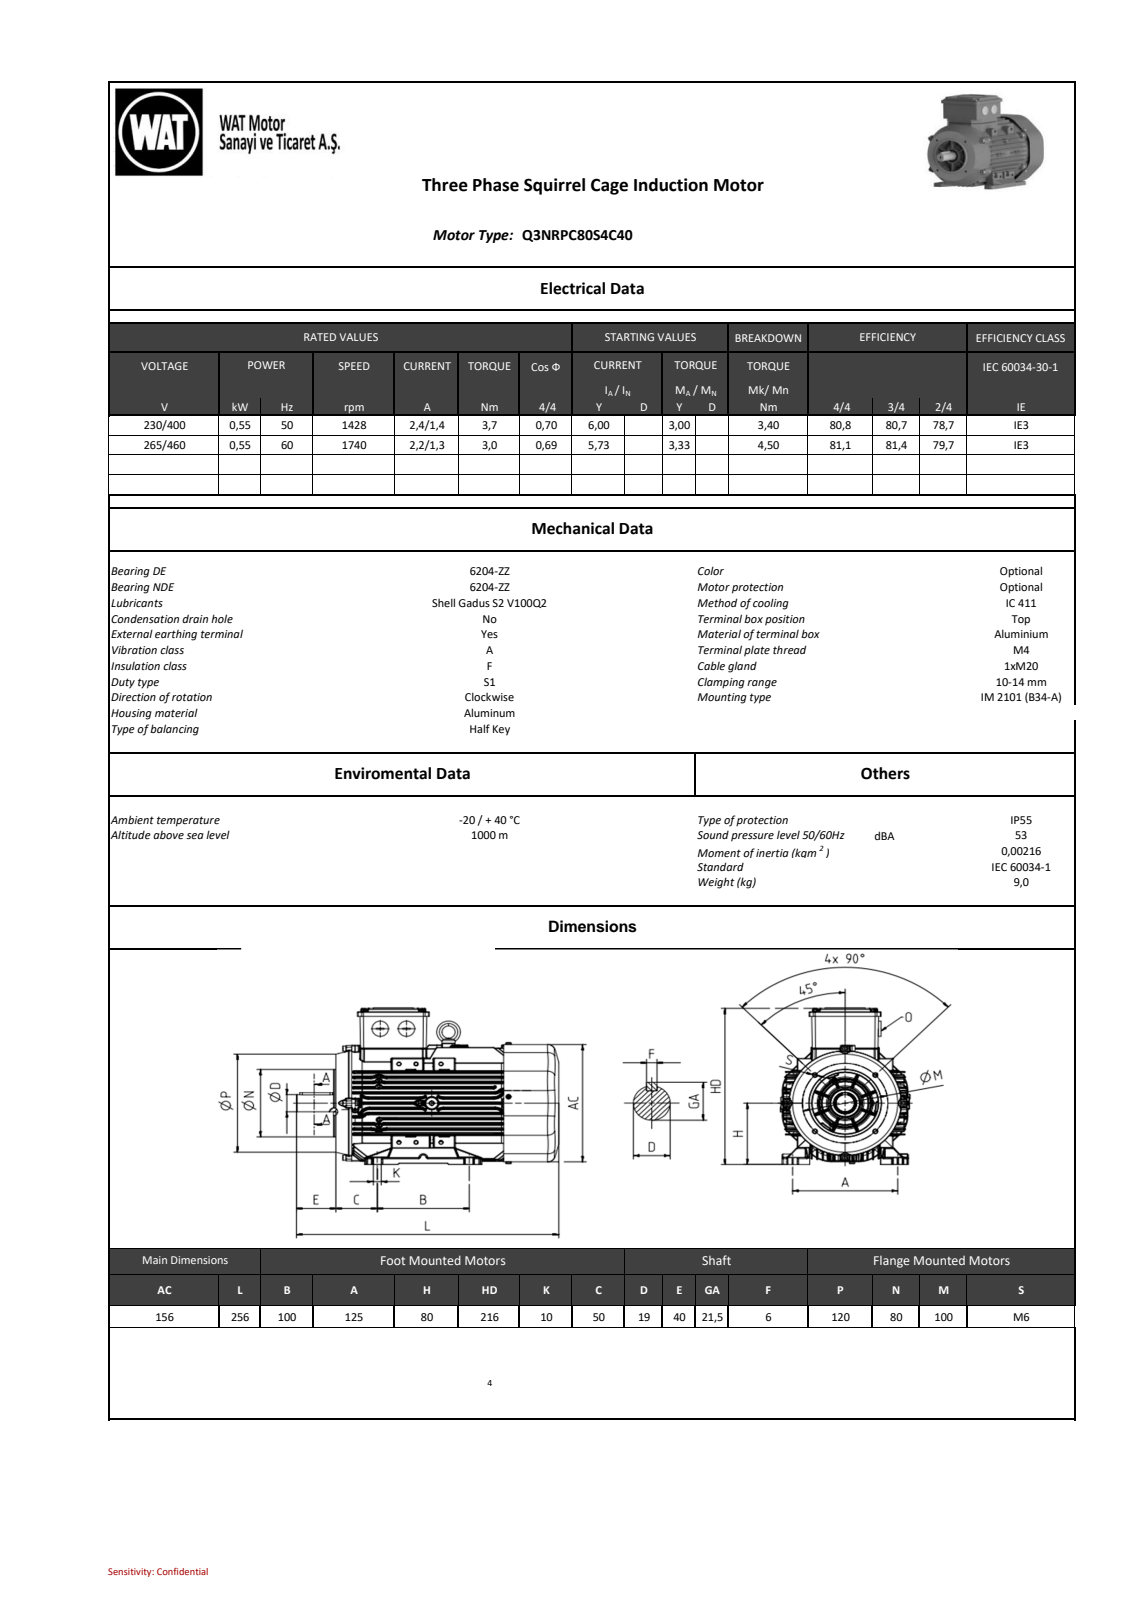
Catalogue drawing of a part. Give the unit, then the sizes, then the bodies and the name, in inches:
Units: inches
Overall size (bounding box): 10.067 × 7.36 × 6.287
Round holes (diameter × count): ⌀0.197 ×4, ⌀0.157 ×1, ⌀0.177 ×1, ⌀0.252 ×1, ⌀0.512 ×1, ⌀1.094 ×1, ⌀1.102 ×1
Round bosses / shafts (diameter × count): ⌀0.335 ×7, ⌀0.315 ×7, ⌀0.197 ×7, ⌀0.362 ×3, ⌀0.787 ×2, ⌀5.291 ×1, ⌀3.15 ×1, ⌀0.748 ×1
Partial cylindrical surfaces — rounded edges, fillets, slot ends (radius × count): R0.02 ×534, R0.039 ×461, R0.031 ×159, R0.016 ×107, R0.008 ×73, R0.03 ×27, R0.118 ×25, R0.157 ×23
Main face-to-face distances: 0.031, 1.181, 1.426, 8.493, 7.067, 0.133, 0.589, 2.367, 2.362, 1.77
Hole centre spacings: 1.969, 1.969, 2.784, 2.784, 3.937, 4.182
Bodies: 0 solids, 5729 faces (1419 planar, 1998 cylindrical, 2312 other)
Part name (STEP PRODUCT): 260320808B12lik2
STEP written by: SIEMENS PLM Software NX 11.0 (AUTOMOTIVE_DESIGN)
